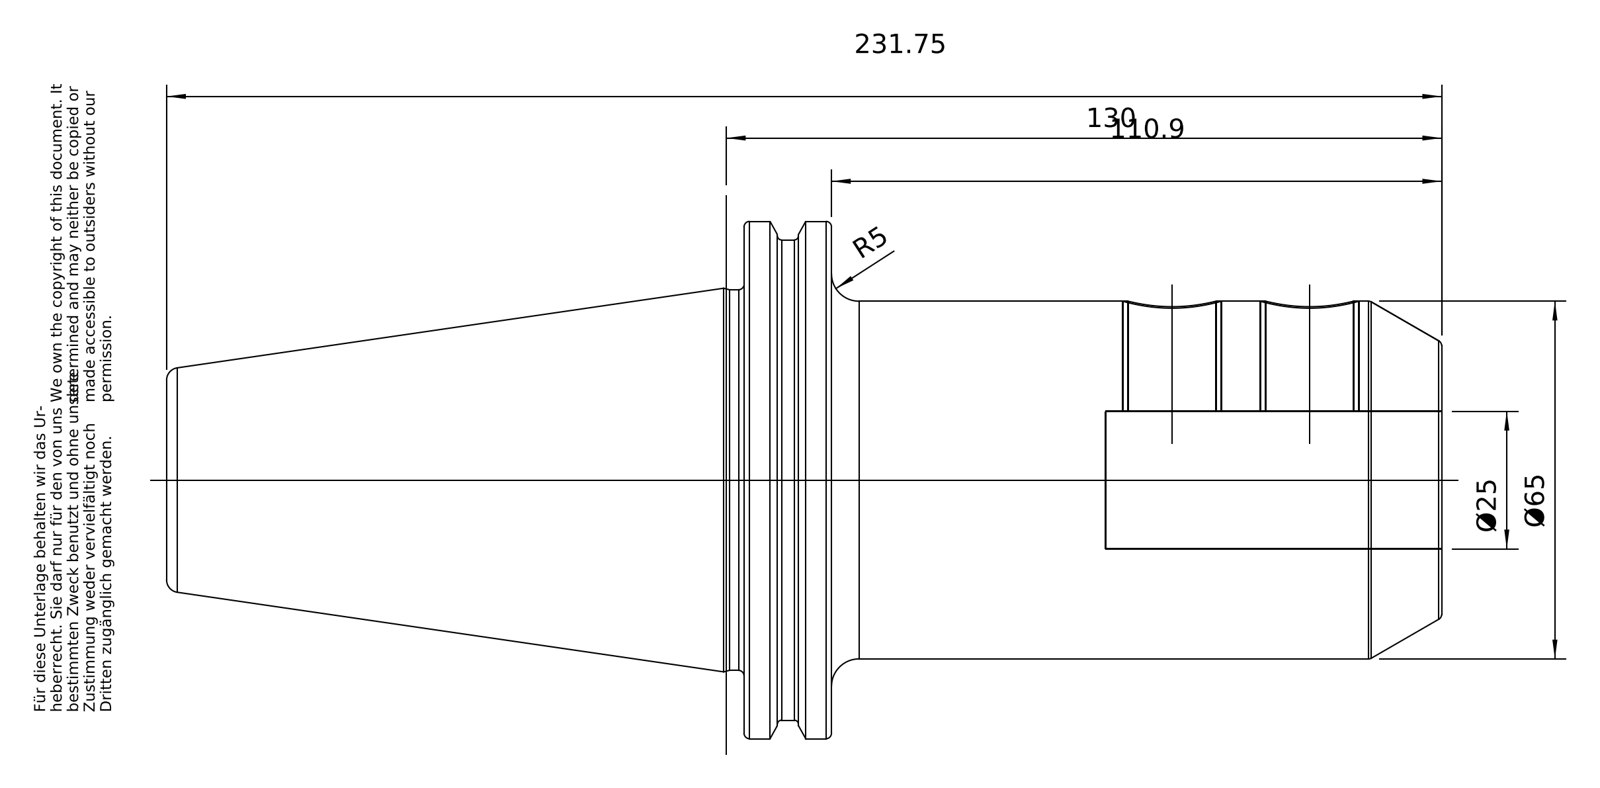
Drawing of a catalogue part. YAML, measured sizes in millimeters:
part_name: "50-304-25"
step_written_by: "PRO/ENGINEER BY PARAMETRIC TECHNOLOGY CORPORATION, 2010430 (CONFIG_CONTROL_DESIGN)"
units: millimeters
bodies: {solids: 1, faces: 108, planar: 22, cylindrical: 36, other: 50}
overall_size: [231.6, 97.47, 94]
volume: 661259
surface_area: 71982
round_holes:
  - {diameter: 16, count: 2}
  - {diameter: 18, count: 2}
  - {diameter: 20.75, count: 1}
  - {diameter: 25, count: 1}
  - {diameter: 25.01, count: 1}
  - {diameter: 25.7, count: 1}
round_bosses_or_shafts:
  - {diameter: 91, count: 1}
  - {diameter: 69.15, count: 1}
  - {diameter: 65, count: 1}
  - {diameter: 24.01, count: 1}
partial_cylinders:
  - {radius: 1.75, count: 5}
  - {radius: 48.74, count: 1}
face_to_face_distances: [15.85, 126.8, 110.95, 65.7, 49.85, 61.1, 104.8, 120.65, 170.5, 231.6]
hole_center_spacings: [25]
